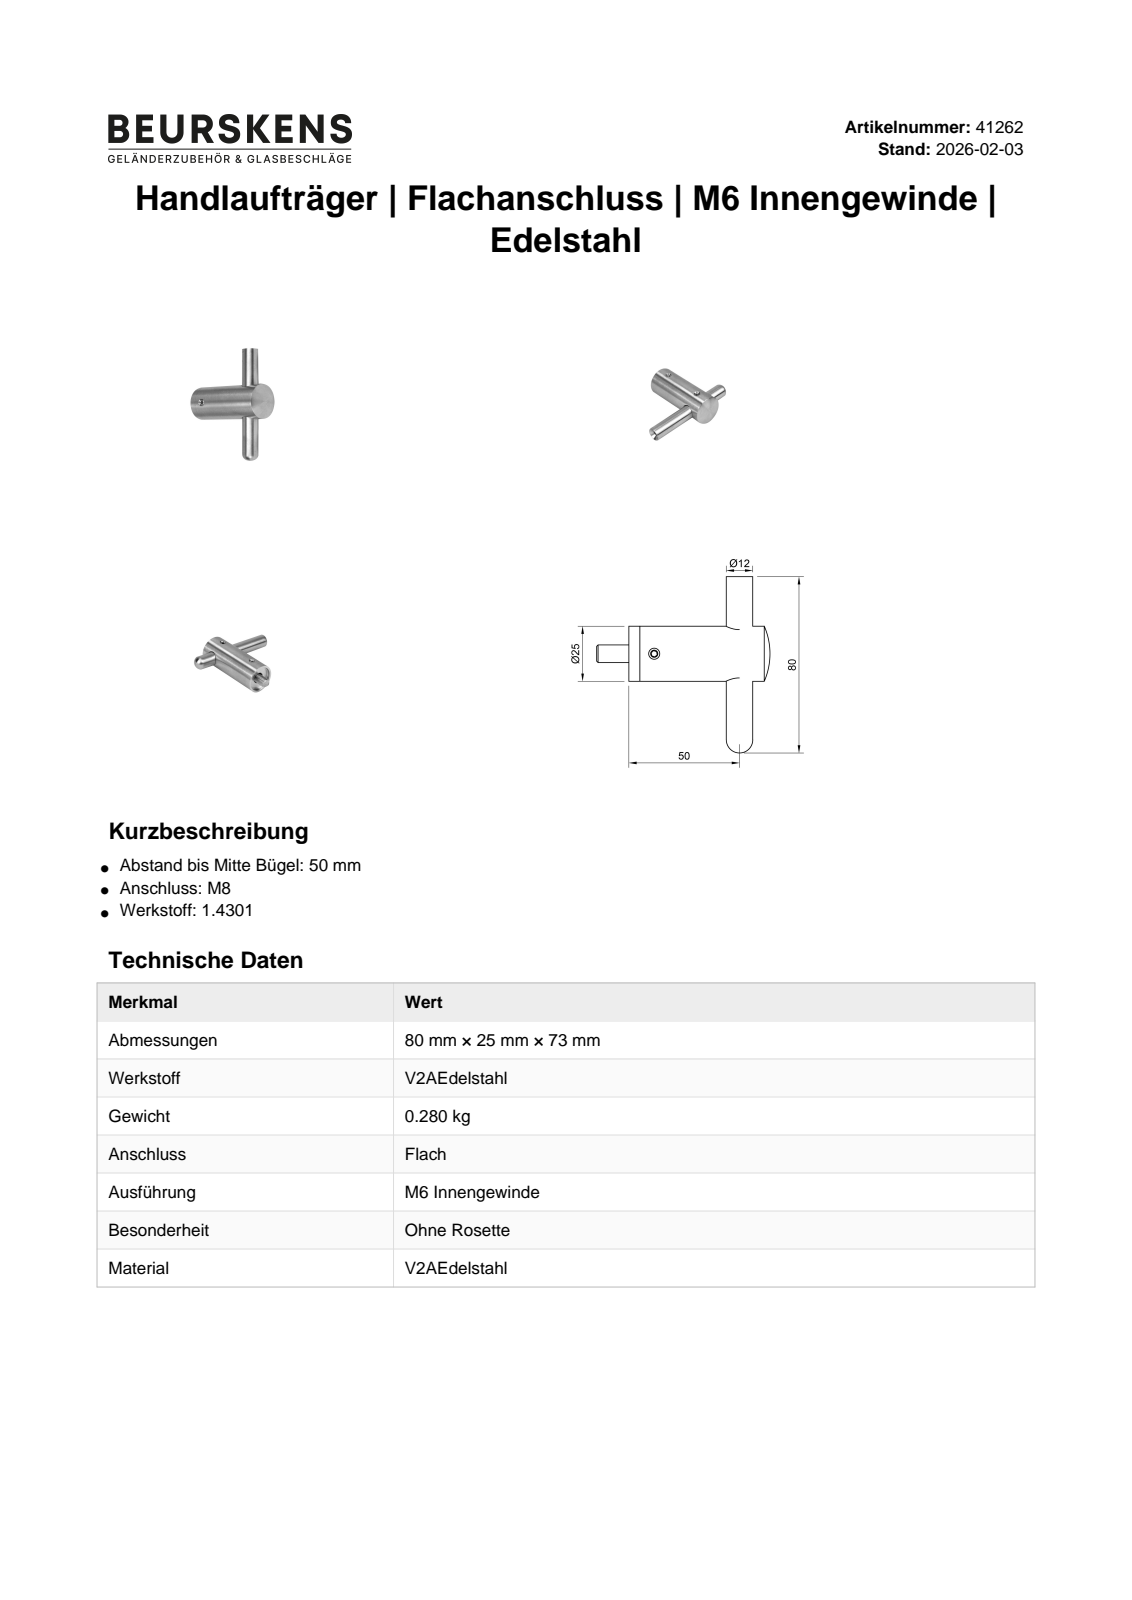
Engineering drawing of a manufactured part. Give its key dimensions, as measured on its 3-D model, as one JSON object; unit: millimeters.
{"part_name": "41262; 41262-01; 41262-02; 41262-03 (+2 more)", "step_written_by": "Autodesk Inventor 2022 (AUTOMOTIVE_DESIGN)", "units": "millimeters", "bodies": {"solids": 8, "faces": 91, "planar": 47, "cylindrical": 19, "other": 25}, "overall_size": [80, 78.6, 26.14], "volume_mm3": 34599, "surface_area_mm2": 14860, "round_holes": [[5, 2], [6, 1], [9, 1], [12, 1], [17.1, 1], [21, 1]], "round_bosses_or_shafts": [[25, 1], [17, 1], [16, 1], [12, 1], [8, 1], [5, 1]], "face_to_face_distances": [2.5, 12.9, 10.4, 5, 15.4, 14.6, 17.1, 19.6, 30, 32.6], "hole_center_spacings": [38.5]}
